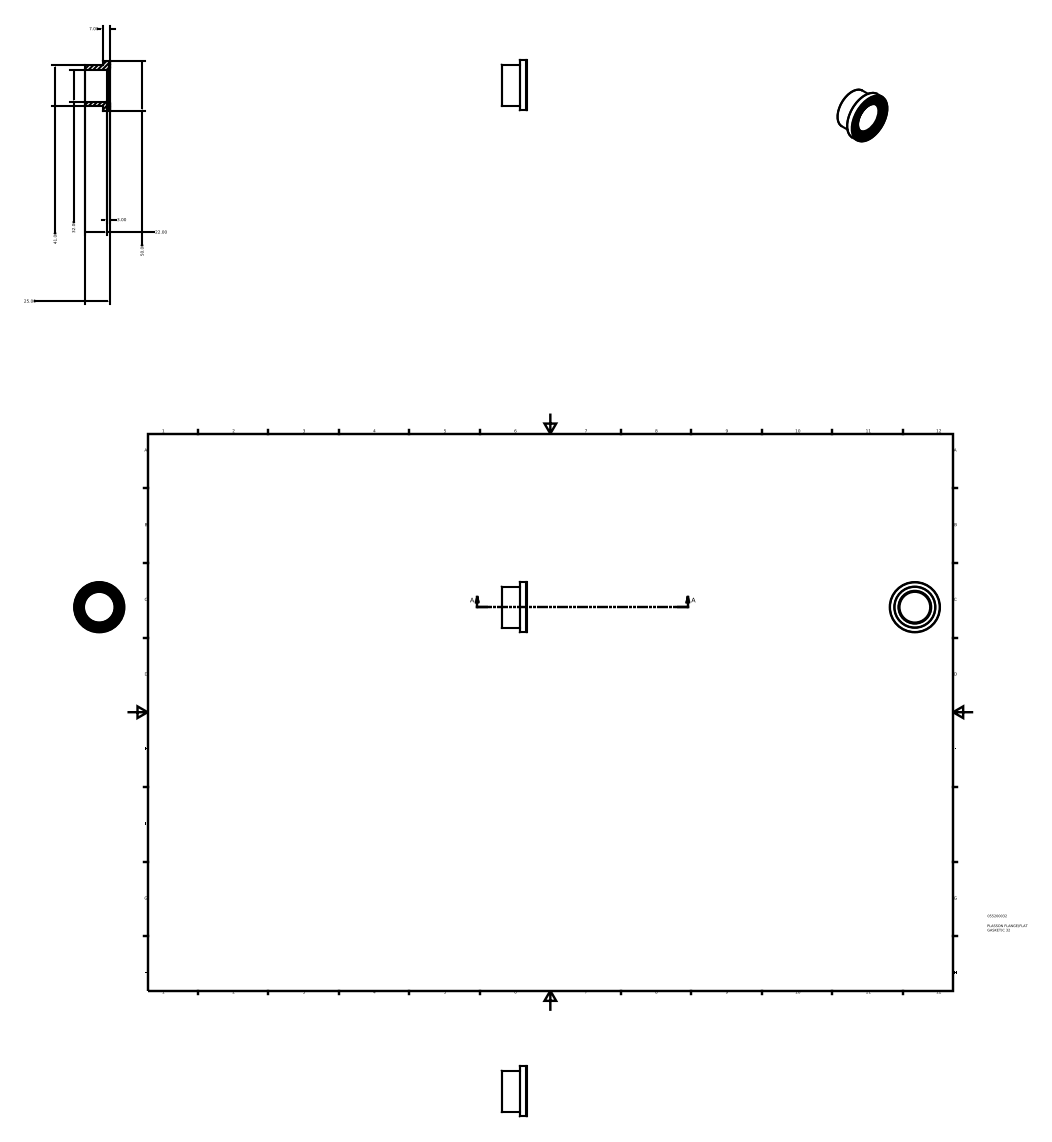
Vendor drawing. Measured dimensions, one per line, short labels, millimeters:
name: 055200032
written by: Autodesk Inventor 2015 (AUTOMOTIVE_DESIGN)
unit: mm
bodies: 1 solid, 33 faces (9 planar, 9 cylindrical, 15 other)
size: 50 × 50 × 25
volume: 17 001 mm³; area: 8 693 mm²
holes: 1× ⌀30.4, 1× ⌀32, 1× ⌀33.67, 1× ⌀40.2, 1× ⌀46.73
bosses: 1× ⌀50, 1× ⌀43.47, 1× ⌀41, 1× ⌀36.93
face distances: 18, 25, 7, 23.95, 5.95, 1.05, 22, 4, 1.95, 3
